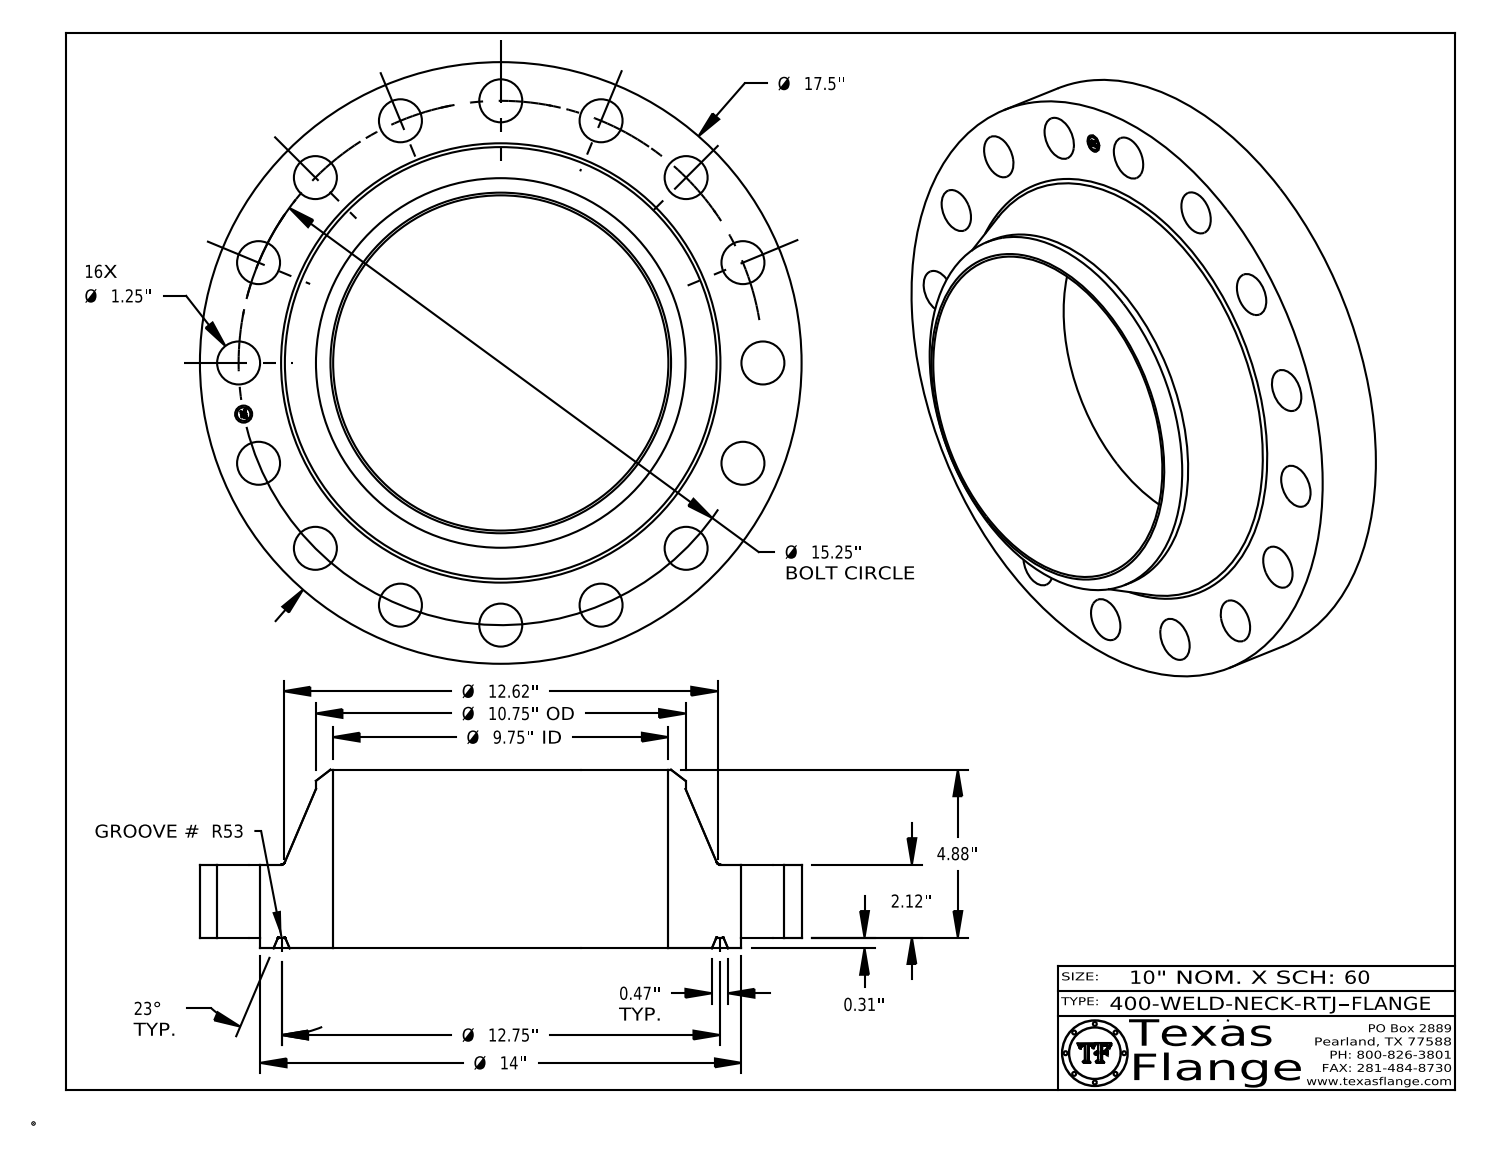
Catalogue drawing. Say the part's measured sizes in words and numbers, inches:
The part is named "400-WELD-NECK-RTJ". Its 3-D file was written by "CATIA V5 STEP AP214 (AUTOMOTIVE_DESIGN)". It is 1 solid with 445 faces: 371 planar, 60 cylindrical and 14 other. Overall it measures 17.5 by 17.5 by 5.193 inches. Its volume is 409.6 cubic inches and its surface area 795.6 square inches. Round holes: 16 of diameter 1.25, 1 of diameter 0.495, 1 of diameter 9.75. Round bosses or shafts: 8 of diameter 0.03, 1 of diameter 17.5, 1 of diameter 14, 1 of diameter 10.75, 1 of diameter 0.39. The main face-to-face distances are 2.12, 0.313, 2.433, 5.193, 4.88, 2.76, 0.015, 2.418, 2.105, 2.775. The hole center spacings are 8.472, 10.783, 14.957, 14.089, 7.625, 2.975, 2.975, 5.836.
